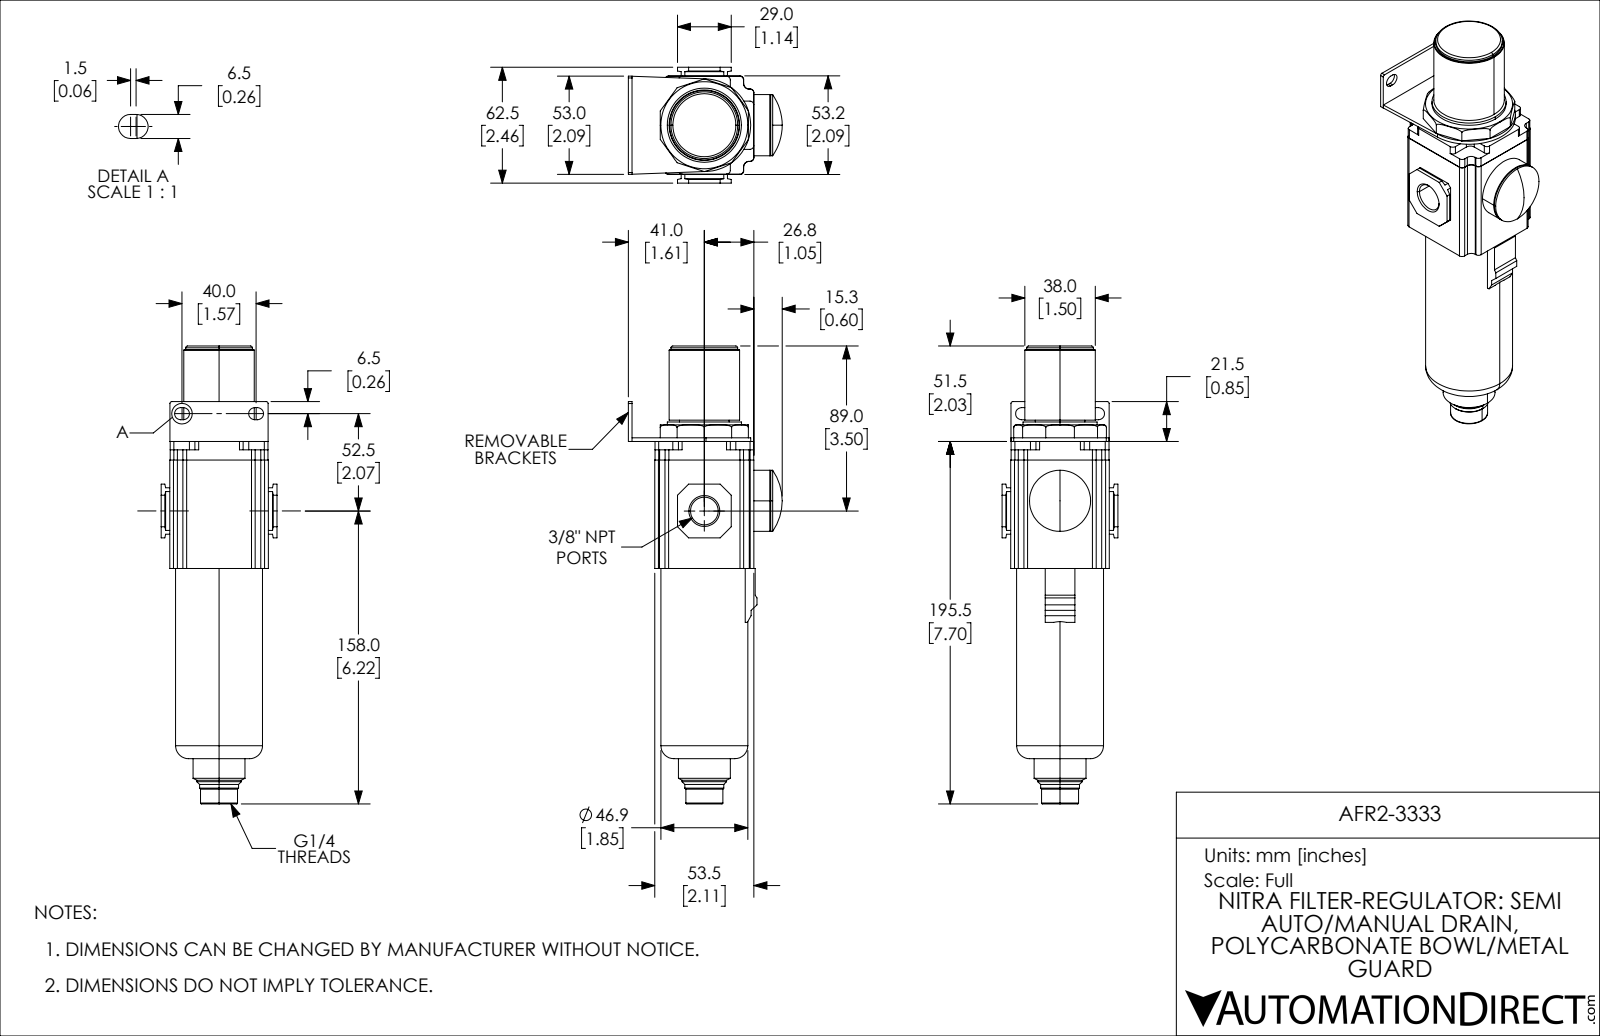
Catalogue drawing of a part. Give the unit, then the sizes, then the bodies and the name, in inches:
Units: inches
Overall size (bounding box): 9.724 × 3.269 × 2.461
Round holes (diameter × count): ⌀0.451 ×1, ⌀0.589 ×1
Round bosses / shafts (diameter × count): ⌀1.846 ×1, ⌀1.575 ×1, ⌀1.496 ×1, ⌀1.417 ×1, ⌀1.299 ×1, ⌀1.102 ×1, ⌀1.054 ×1, ⌀0.945 ×1
Partial cylindrical surfaces — rounded edges, fillets, slot ends (radius × count): R0.079 ×24, R0.118 ×12, R0.128 ×4, R0.039 ×2, R0.984 ×1
Main face-to-face distances: 0.079, 2.094, 2.106, 0.561, 0.183, 2.278, 0.482, 2.667, 2.028, 1.949
Volume: 27.43 in³ · Surface area: 80.97 in²
Bodies: 1 solid, 221 faces (124 planar, 71 cylindrical, 26 other)
Part name (STEP PRODUCT): AFR2-3333
STEP written by: SolidWorks 2019 (CONFIG_CONTROL_DESIGN)
